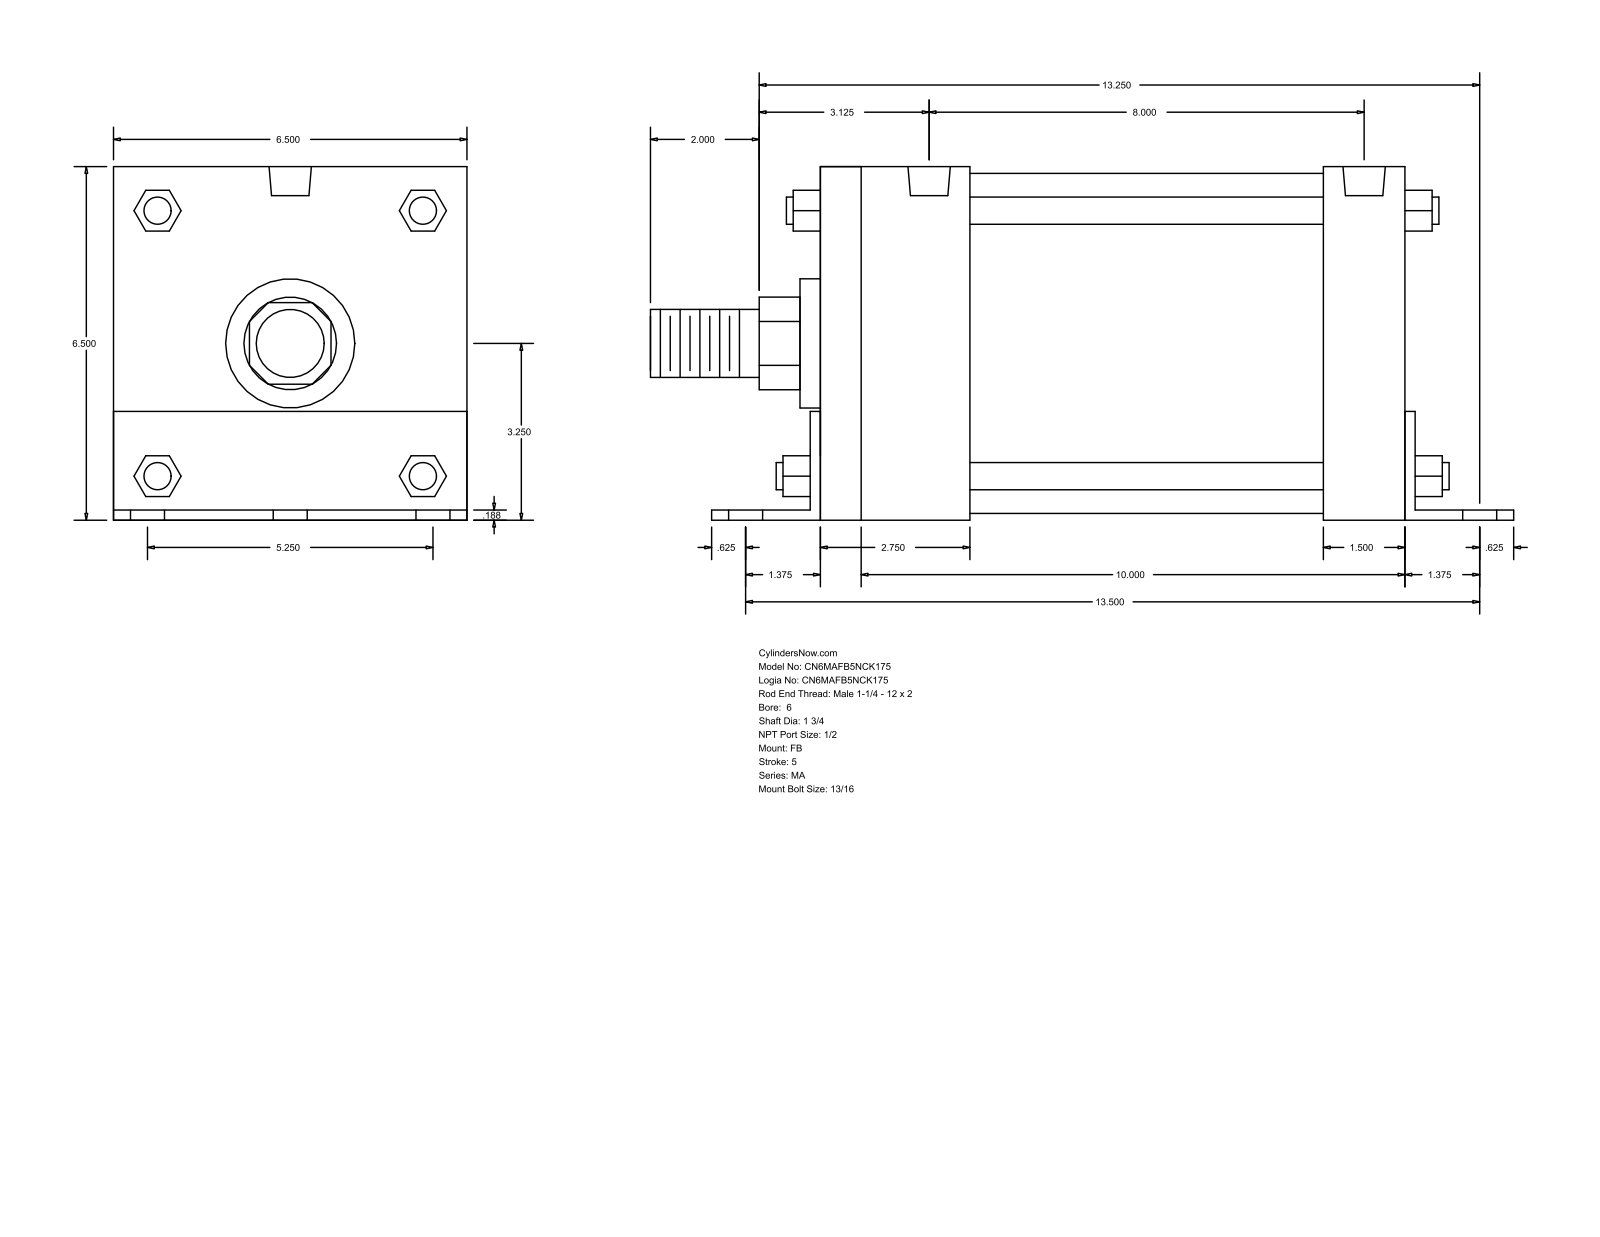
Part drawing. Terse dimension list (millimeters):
name: MA_FB__0600_1.75
written by: GSSL Pune (CONFIG_CONTROL_DESIGN)
unit: mm
bodies: 0 solids, 140 faces (105 planar, 35 cylindrical, 0 other)
size: 403.23 × 165.15 × 165.1
holes: 6× ⌀20.64, 4× ⌀17.46, 2× ⌀19.77
bosses: 4× ⌀12.7, 1× ⌀158.75, 1× ⌀60.33, 1× ⌀44.45, 1× ⌀31.75
rounds: 1× R21.63, 1× R32.05
face distances: 165.1, 4.76, 273.05, 165.15, 4.71, 160.39, 69.85, 74.61, 4.77, 38.1
hole spacings: 66.67, 349.32, 342.9, 85.78, 108.6, 133.34, 203.19, 265.67
